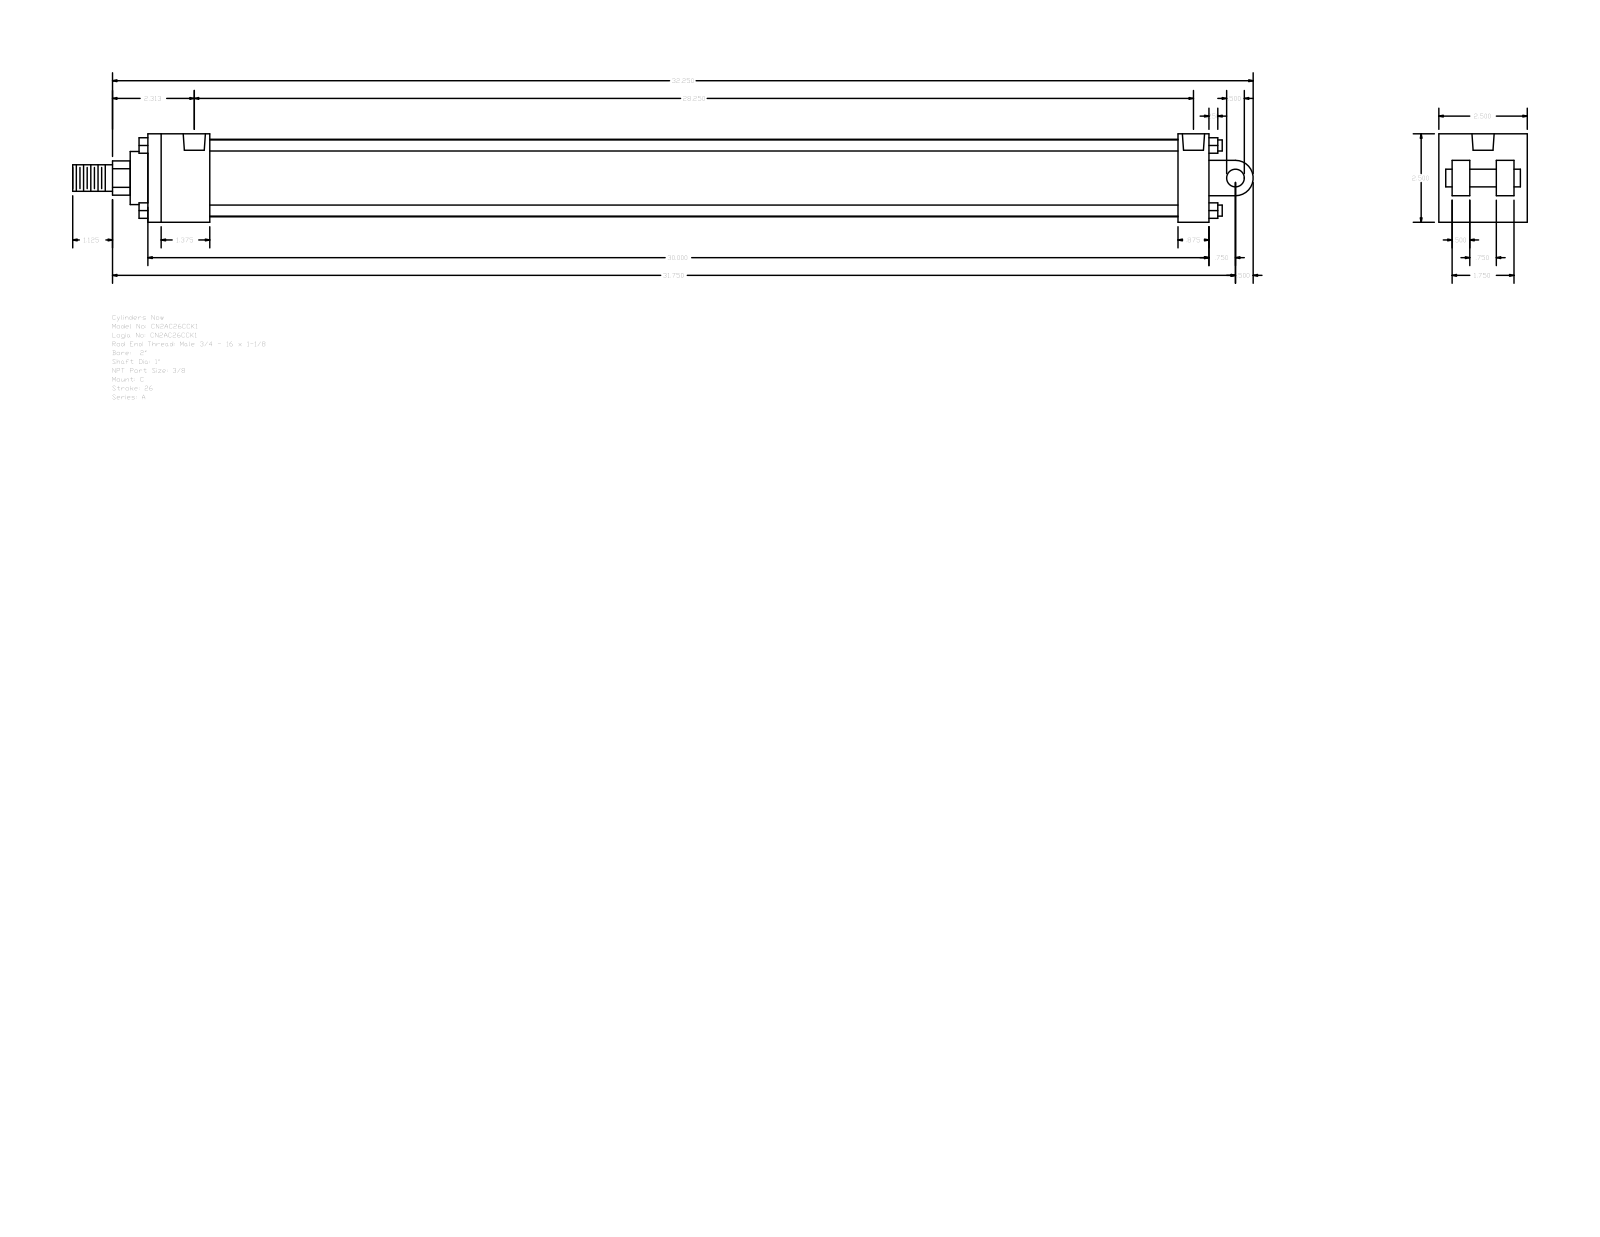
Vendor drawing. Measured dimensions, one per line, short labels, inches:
name: A_C__0200_1
written by: GSSL Pune (CONFIG_CONTROL_DESIGN)
unit: in
bodies: 0 solids, 135 faces (102 planar, 33 cylindrical, 0 other)
size: 33.375 × 2.5 × 2.5
holes: 4× ⌀0.219, 2× ⌀0.627
bosses: 4× ⌀0.313, 1× ⌀2.19, 1× ⌀1.5, 1× ⌀1, 1× ⌀0.75, 1× ⌀0.5
rounds: 1× R0.484, 1× R0.5
face distances: 2.5, 30, 1.75, 0.5, 0.375, 28.25, 29.125, 27.375, 0.875, 2.125
hole spacings: 28.031, 0.063, 0.157, 28.093, 28.187, 28.25
